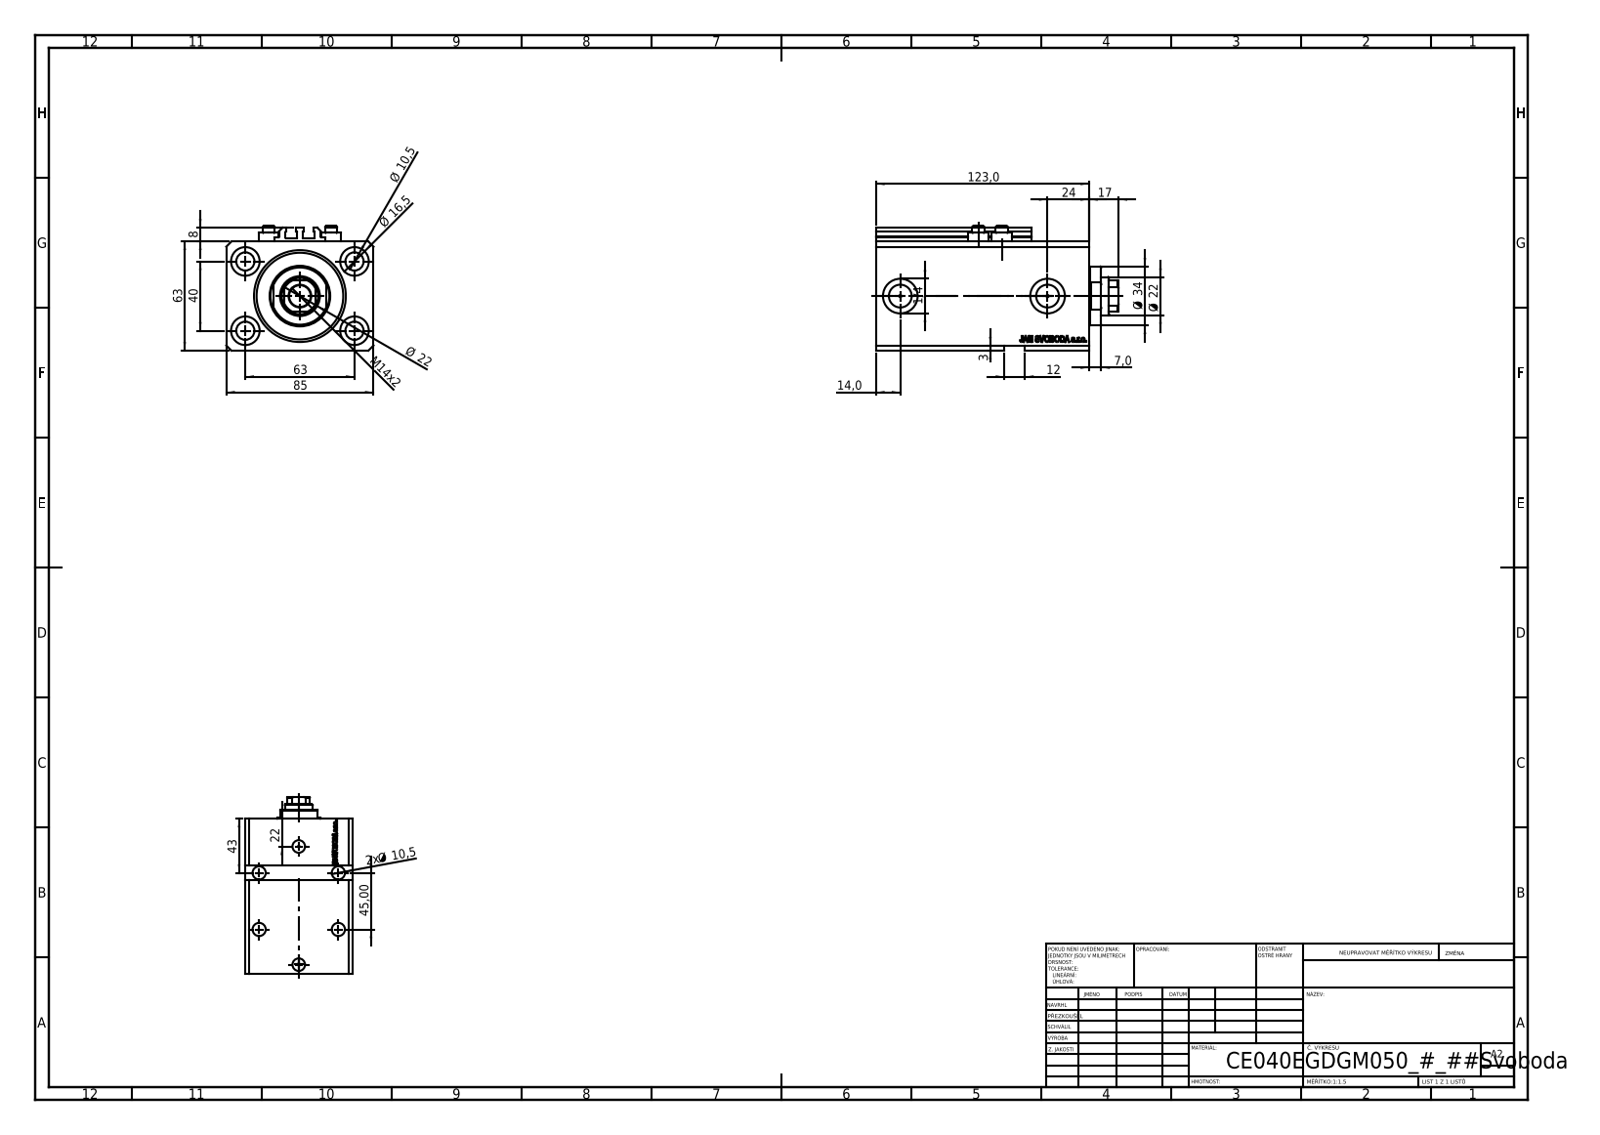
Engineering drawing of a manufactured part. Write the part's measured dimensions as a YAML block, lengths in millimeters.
part_name: "ALLEN BOLT V250CE; V250CE_C_VCP; V250CE_VC_E; V250CE_E_Body"
step_written_by: "SolidWorks 2019 (CONFIG_CONTROL_DESIGN)"
units: millimeters
bodies: {solids: 8, faces: 1123, planar: 539, cylindrical: 158, other: 426}
overall_size: [140, 85, 72]
volume: 553016
surface_area: 120484
round_holes:
  - {diameter: 10.5, count: 8}
  - {diameter: 1.25, count: 4}
  - {diameter: 4, count: 4}
  - {diameter: 16.5, count: 4}
  - {diameter: 10, count: 2}
  - {diameter: 13.16, count: 2}
  - {diameter: 20, count: 2}
  - {diameter: 12.5, count: 1}
  - {diameter: 22, count: 1}
  - {diameter: 40, count: 1}
  - {diameter: 53, count: 1}
round_bosses_or_shafts:
  - {diameter: 11.6, count: 4}
  - {diameter: 7, count: 4}
  - {diameter: 34, count: 1}
partial_cylinders:
  - {radius: 0.2, count: 10}
  - {radius: 10.5, count: 1}
face_to_face_distances: [63, 85, 123, 17, 106, 11.4, 94.6, 111.6, 3, 56]
hole_center_spacings: [37.31, 63, 13.6, 15.4, 24.96, 27.54, 33.62, 36]
